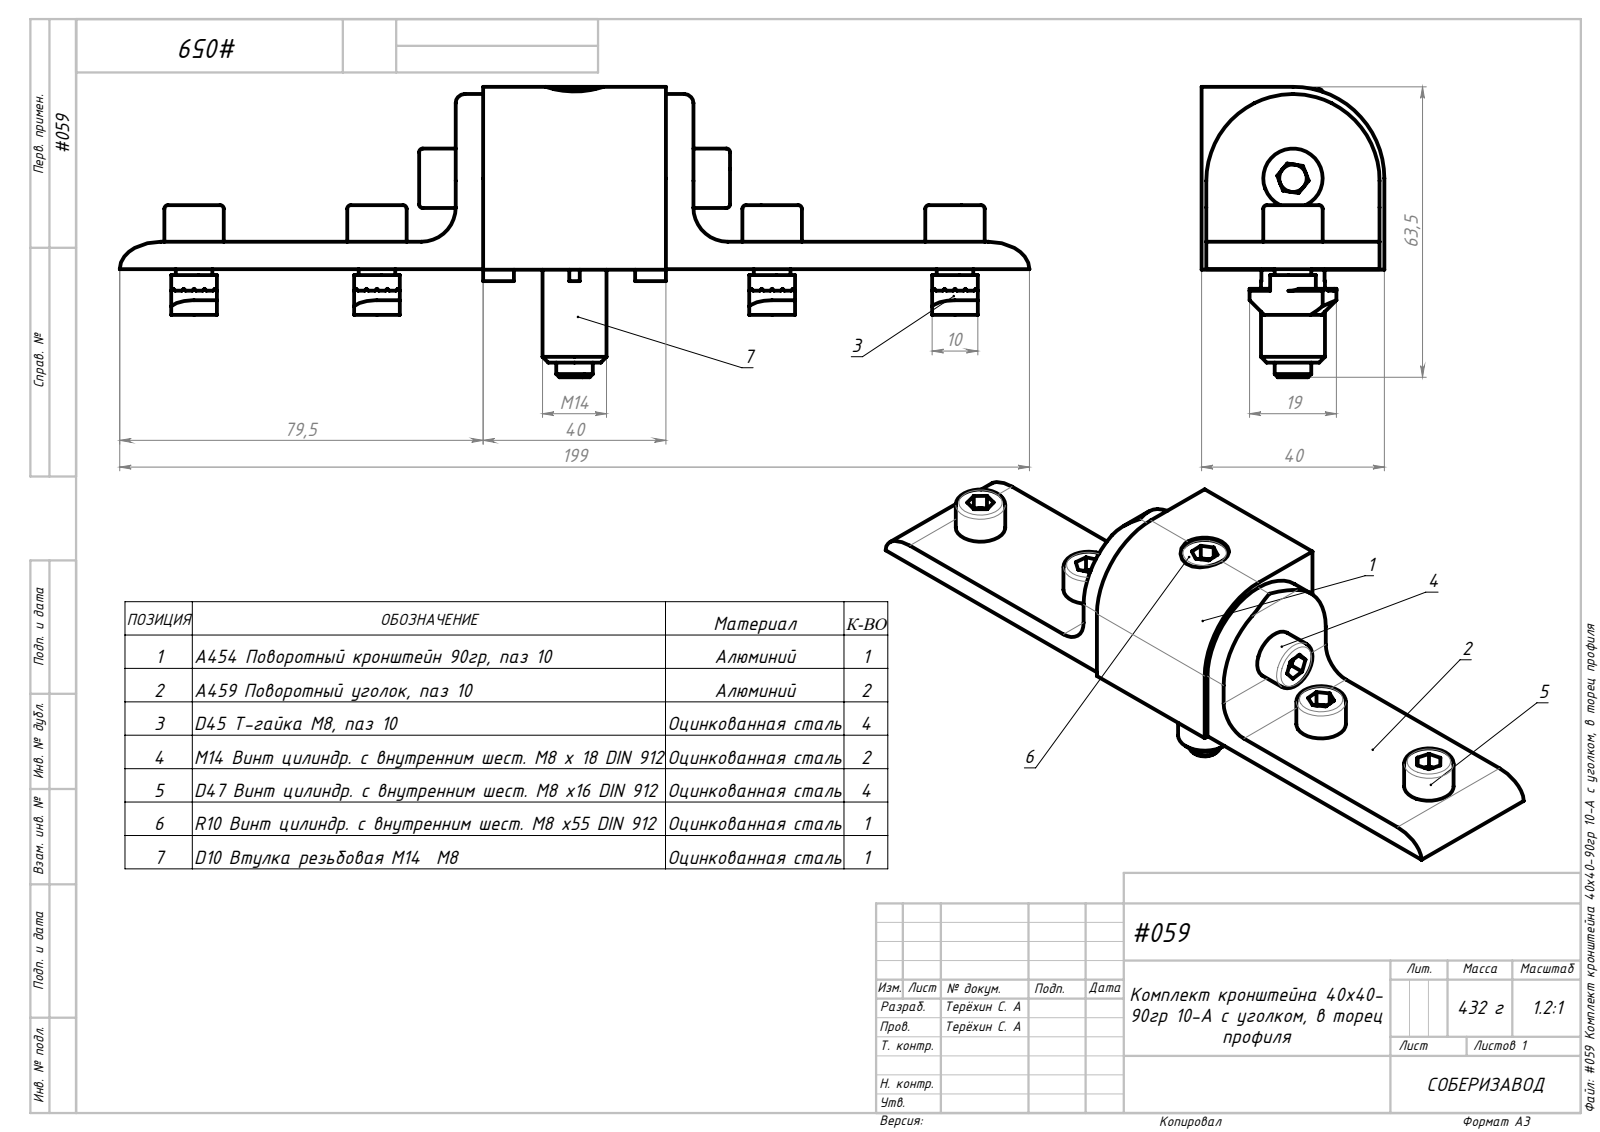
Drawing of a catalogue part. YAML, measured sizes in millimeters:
part_name: "#059 Комплект кронштейна 40х40-90гр 10-A с уголком, в торец профиля; A459 Поворотный уголок, паз 10; M14 Винт цилиндр. с внутренним шест. М8 х 18 DIN 912; A454 Поворотный кронштейн 90гр, паз 10 (+4 more)"
step_written_by: "SolidWorks 2021 (AUTOMOTIVE_DESIGN)"
units: millimeters
bodies: {solids: 15, faces: 466, planar: 293, cylindrical: 85, other: 88}
overall_size: [199, 63.5, 40]
volume: 123573
surface_area: 43707
round_holes:
  - {diameter: 8.35, count: 5}
  - {diameter: 6.7, count: 4}
  - {diameter: 7, count: 1}
  - {diameter: 7.3, count: 1}
  - {diameter: 8.25, count: 1}
  - {diameter: 12.7, count: 1}
round_bosses_or_shafts:
  - {diameter: 13, count: 6}
  - {diameter: 8, count: 6}
  - {diameter: 14, count: 1}
partial_cylinders:
  - {radius: 5.67, count: 8}
  - {radius: 6, count: 8}
  - {radius: 2, count: 2}
  - {radius: 7.5, count: 2}
  - {radius: 19, count: 2}
  - {radius: 20, count: 1}
face_to_face_distances: [6, 40, 1.05, 38.95, 46, 6.13, 37.9, 10, 52, 39.87]
hole_center_spacings: [40, 40.01, 43.22, 43.23, 83.23, 86.45, 126.45, 126.46]
